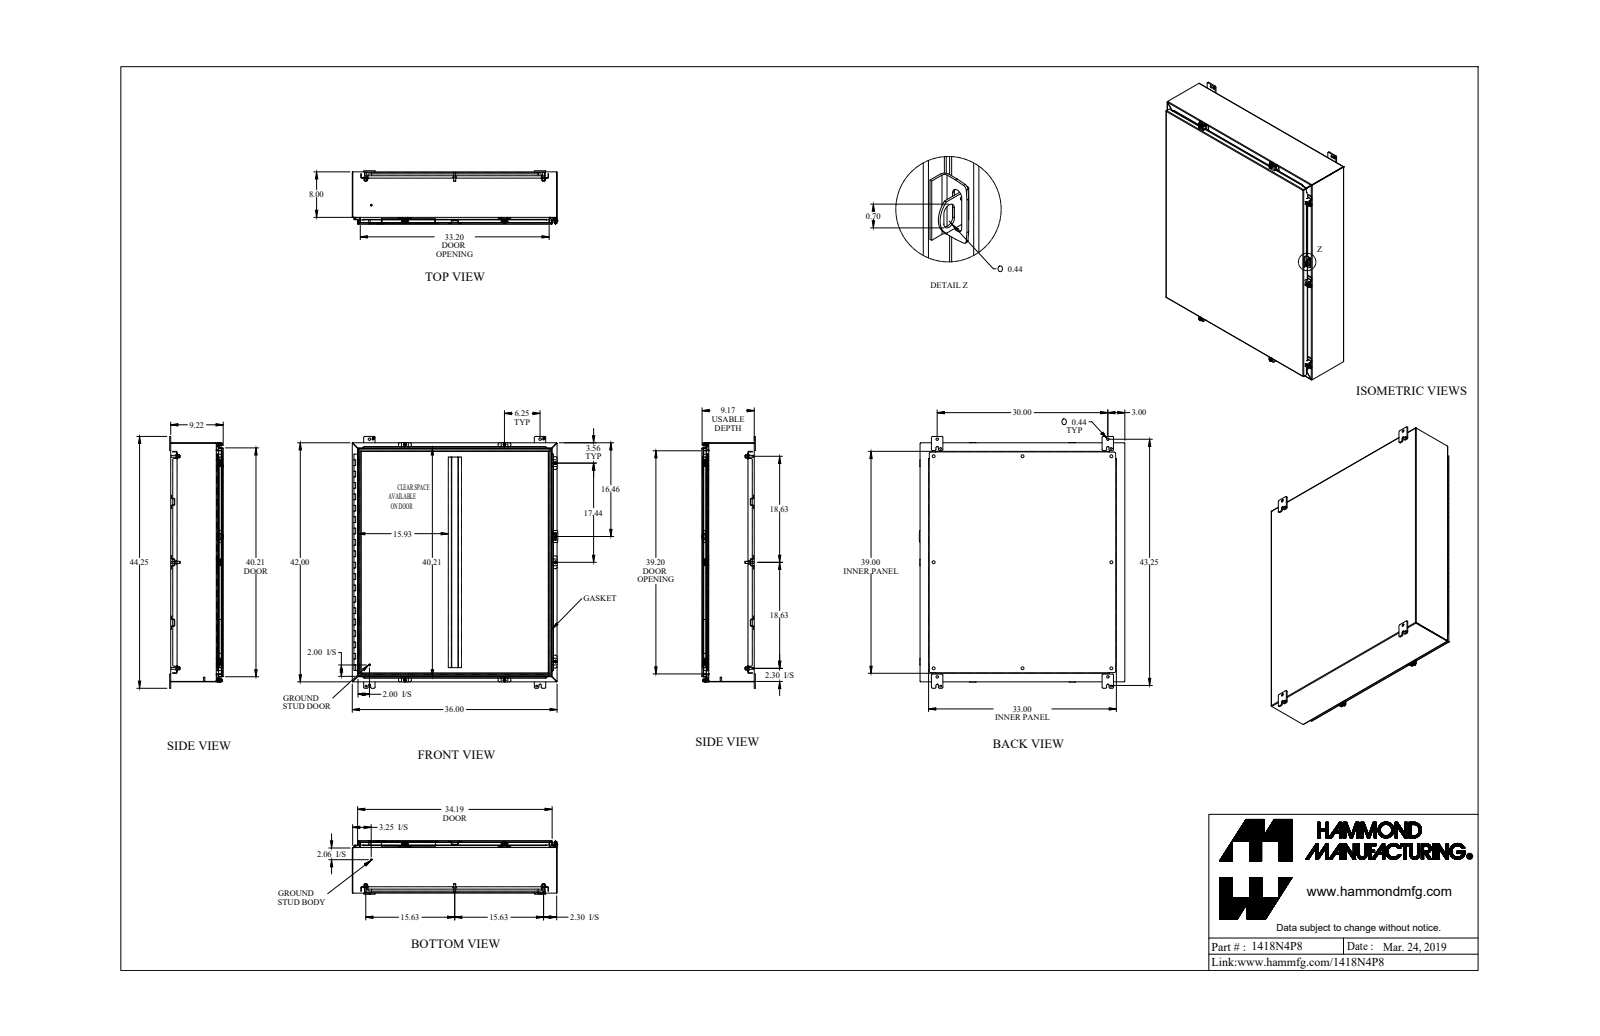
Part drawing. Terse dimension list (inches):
name: 1418N4P8_Default
written by: SolidWorks 2019 (CONFIG_CONTROL_DESIGN)
unit: in
bodies: 65 solids, 2241 faces (1303 planar, 807 cylindrical, 131 other)
size: 44.25 × 36.126 × 9.437
volume: 520.2 in³; area: 13 544 in²
holes: 8× ⌀0.5, 7× ⌀0.213, 7× ⌀0.375, 5× ⌀0.265, 5× ⌀0.307, 4× ⌀0.313, 4× ⌀0.437, 3× ⌀0.445, 2× ⌀0.265, 2× ⌀0.445, 1× ⌀0.125, 1× ⌀0.187
bosses: 8× ⌀0.65, 8× ⌀0.375, 8× ⌀0.33, 7× ⌀0.5, 7× ⌀0.39, 7× ⌀0.244, 5× ⌀1, 2× ⌀0.281
rounds: 44× R0.25, 42× R0.188, 33× R0.048, 33× R0.143, 24× R0.036, 24× R0.108, 16× R0.116, 14× R0.141
face distances: 0.072, 0.072, 9.071, 9.143, 9.143, 9.215, 8.111, 8.039, 1.032, 1.104
hole spacings: 7.196, 15.625, 24.468, 18.625, 37.25, 39.97, 40.394, 46.309
